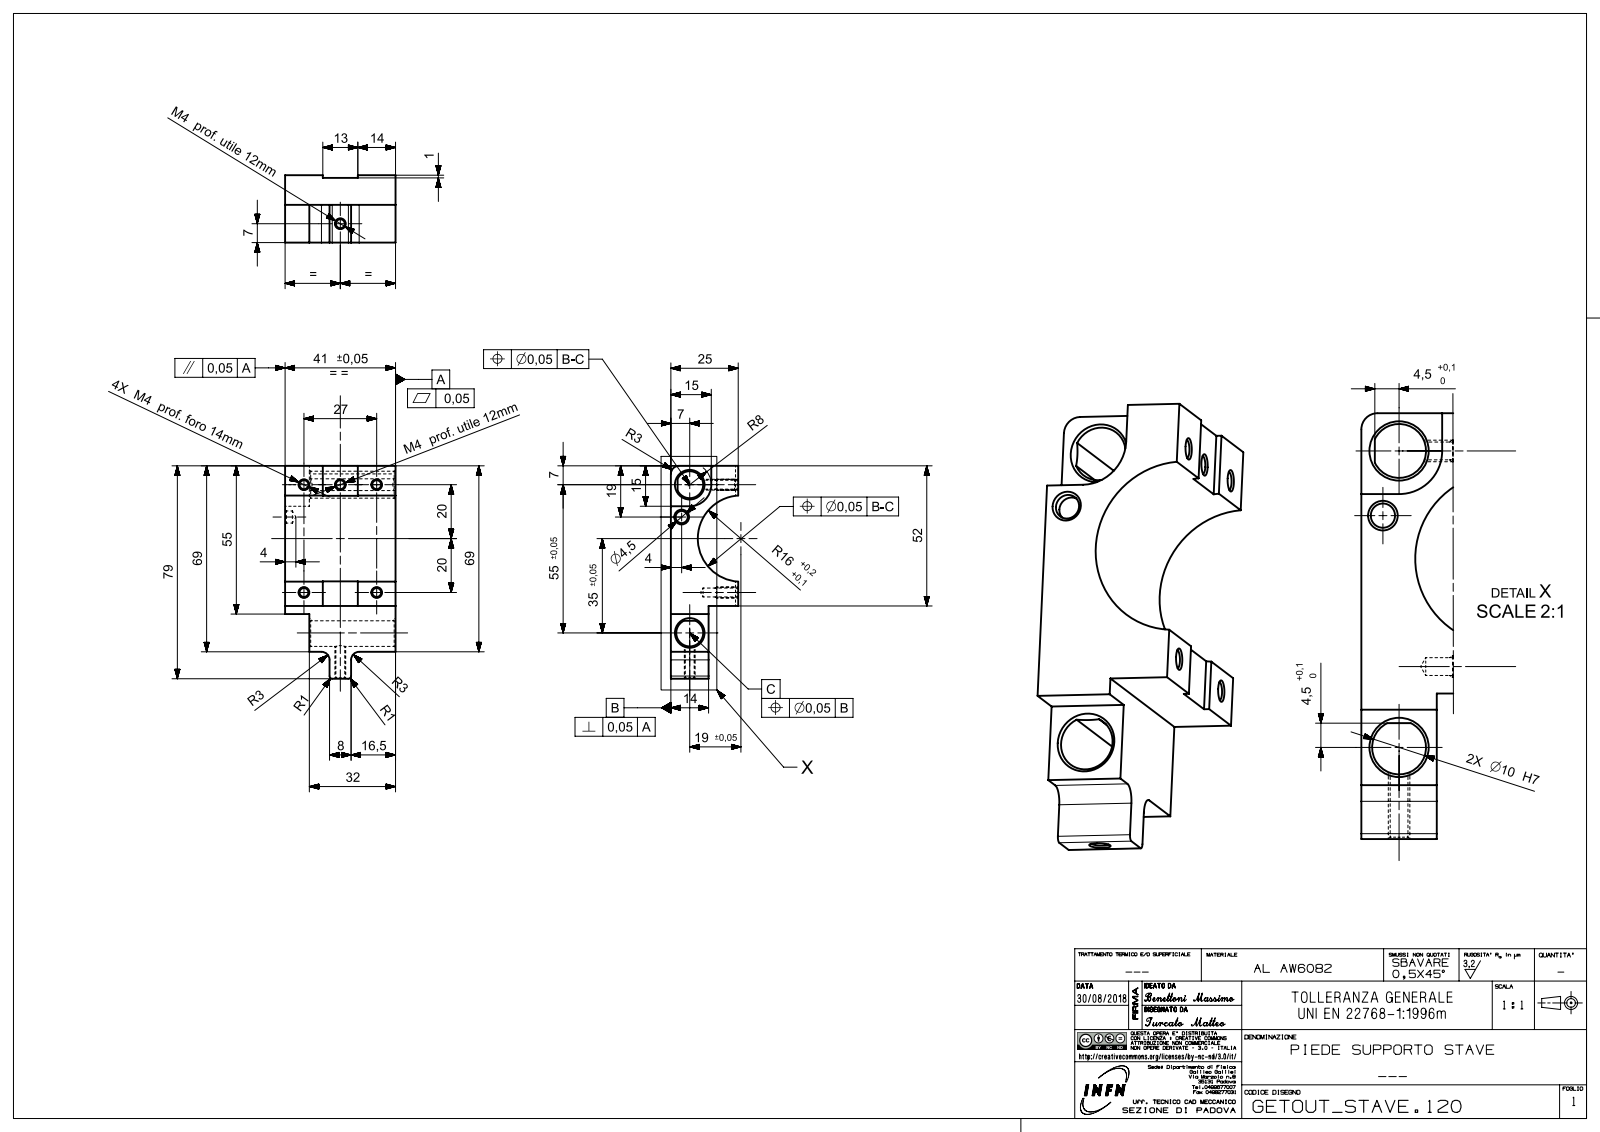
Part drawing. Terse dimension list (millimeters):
name: bezA730AE56cd2l
written by: SIEMENS PLM Software NX 12.0 (AUTOMOTIVE_DESIGN)
unit: mm
bodies: 1 solid, 60 faces (29 planar, 17 cylindrical, 14 other)
size: 79 × 41 × 25
volume: 39 446 mm³; area: 13 135 mm²
holes: 6× ⌀3.3, 2× ⌀10, 1× ⌀4.5
rounds: 3× R3, 2× R1, 1× R8, 1× R16
face distances: 14, 41, 25, 11, 52, 10, 24, 1, 2.5, 9
hole spacings: 13.5, 27, 40, 42.22, 48.26, 12.37, 43.1, 55
